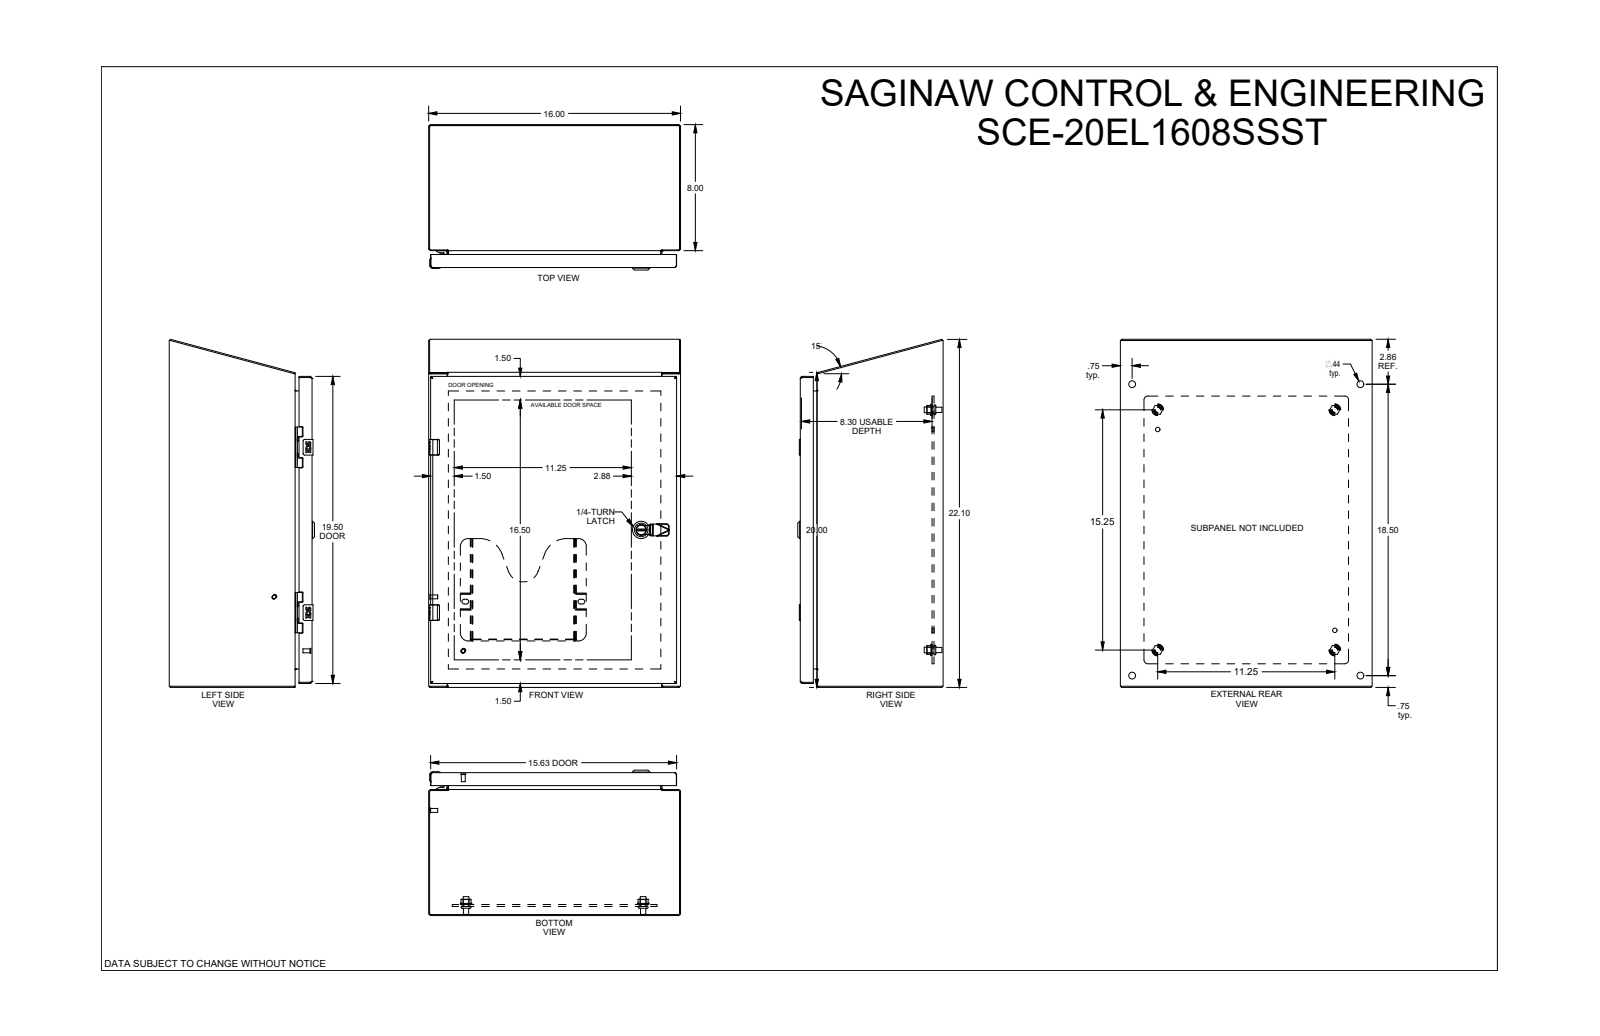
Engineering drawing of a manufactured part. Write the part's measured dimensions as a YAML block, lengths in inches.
part_name: "SCE-20EL1608SSST"
step_written_by: "SolidWorks 2021 (AUTOMOTIVE_DESIGN)"
units: inches
bodies: {solids: 26, faces: 1333, planar: 619, cylindrical: 485, other: 229}
overall_size: [22.106, 16, 9.935]
volume: 146.4
surface_area: 3585
round_holes:
  - {diameter: 0.172, count: 4}
  - {diameter: 0.205, count: 4}
  - {diameter: 0.244, count: 4}
  - {diameter: 0.266, count: 4}
  - {diameter: 0.437, count: 4}
  - {diameter: 0.5, count: 4}
  - {diameter: 0.187, count: 2}
  - {diameter: 0.218, count: 2}
  - {diameter: 0.281, count: 2}
  - {diameter: 0.375, count: 2}
  - {diameter: 0.375, count: 2}
  - {diameter: 0.193, count: 1}
round_bosses_or_shafts:
  - {diameter: 0.375, count: 4}
  - {diameter: 0.33, count: 4}
  - {diameter: 0.25, count: 4}
  - {diameter: 0.248, count: 4}
  - {diameter: 1.102, count: 1}
  - {diameter: 0.78, count: 1}
  - {diameter: 0.63, count: 1}
  - {diameter: 0.504, count: 1}
partial_cylinders:
  - {radius: 0.015, count: 28}
  - {radius: 0.04, count: 23}
  - {radius: 0.22, count: 16}
  - {radius: 0.06, count: 15}
  - {radius: 0.07, count: 10}
  - {radius: 0.145, count: 10}
  - {radius: 0.03, count: 8}
  - {radius: 0.031, count: 8}
face_to_face_distances: [0.075, 0.06, 15.925, 0.075, 9.068, 8.993, 9.008, 8.933, 0.125, 0.5]
hole_center_spacings: [10.5, 0.985, 12.959, 14.867, 15.129, 20.123, 13.139, 13.53]
